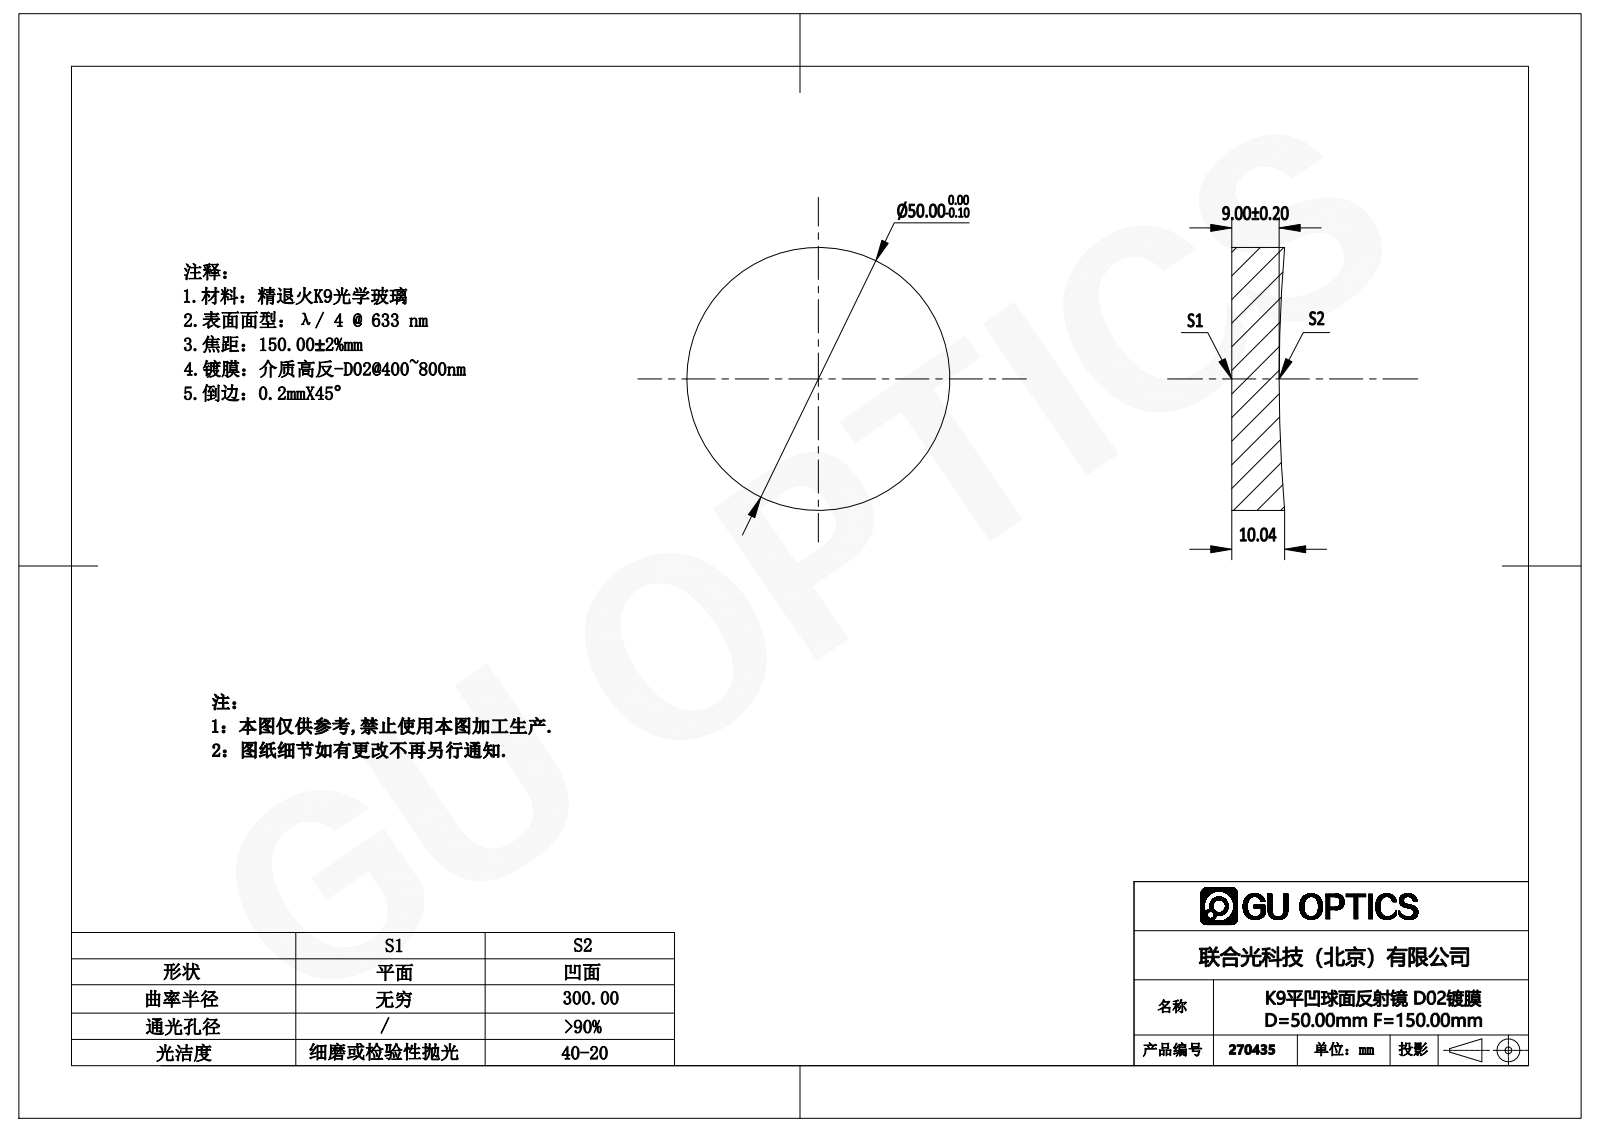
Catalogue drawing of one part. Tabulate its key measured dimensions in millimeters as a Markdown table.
| quantity | value |
| --- | --- |
| part name | 270045 |
| STEP written by | SolidWorks 2016 (AUTOMOTIVE_DESIGN) |
| units | millimeters |
| bodies | 1 solid, 5 faces (1 planar, 2 cylindrical, 2 other) |
| overall size | 50 × 50 × 10.04 |
| volume | 18 695 mm³ |
| surface area | 5 508 mm² |
| round bosses / shafts (diameter × count) | 50 × 1 |
